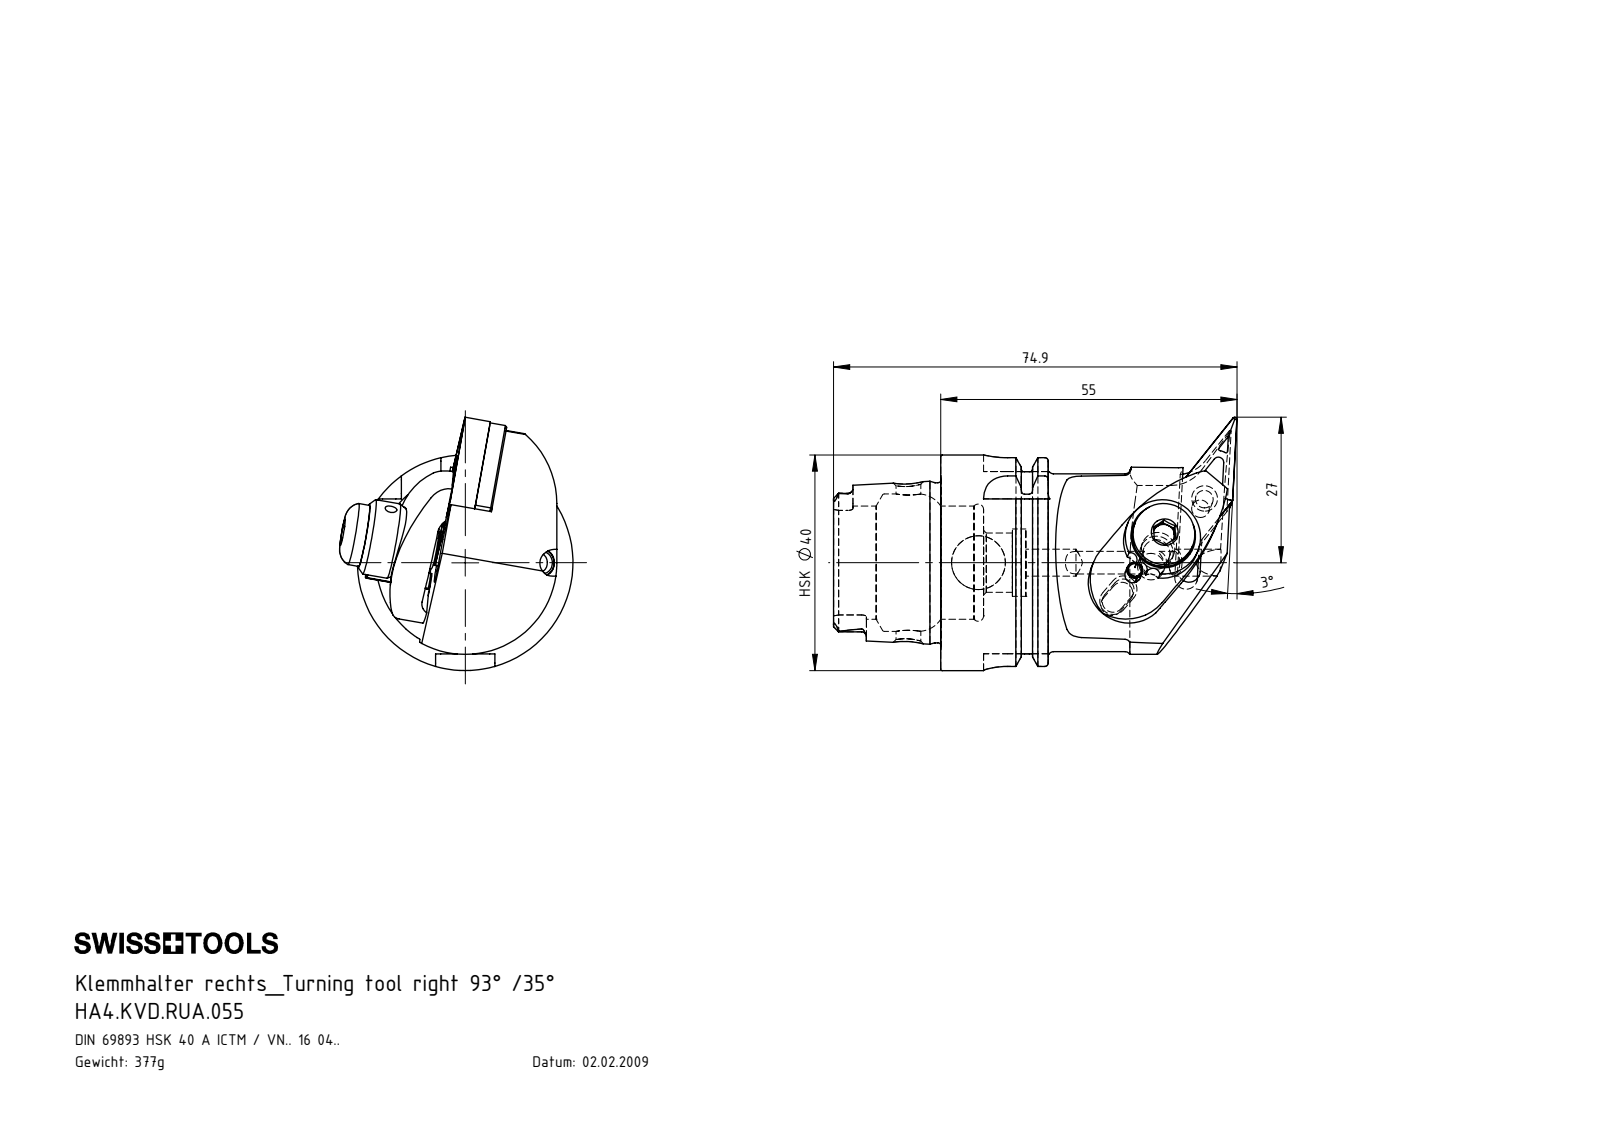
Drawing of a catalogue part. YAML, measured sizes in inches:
part_name: "WCC-ER3.102.024_C; WCC-ER5.102.005_A; VNMG160404; WCC-ER2.001.010_A (+7 more)"
step_written_by: "SolidWorks 2017 (AUTOMOTIVE_DESIGN)"
units: inches
bodies: {solids: 11, faces: 467, planar: 126, cylindrical: 154, other: 187}
overall_size: [2.949, 1.85, 1.706]
volume: 2.898
surface_area: 29.38
round_holes:
  - {diameter: 0.079, count: 3}
  - {diameter: 0.197, count: 2}
  - {diameter: 0.276, count: 2}
  - {diameter: 0.094, count: 1}
  - {diameter: 0.118, count: 1}
  - {diameter: 0.13, count: 1}
  - {diameter: 0.15, count: 1}
  - {diameter: 0.157, count: 1}
  - {diameter: 0.165, count: 1}
  - {diameter: 0.181, count: 1}
  - {diameter: 0.195, count: 1}
  - {diameter: 0.244, count: 1}
round_bosses_or_shafts:
  - {diameter: 0.197, count: 2}
  - {diameter: 0.118, count: 2}
  - {diameter: 1.575, count: 1}
  - {diameter: 1.368, count: 1}
  - {diameter: 1.299, count: 1}
  - {diameter: 1.17, count: 1}
  - {diameter: 0.551, count: 1}
  - {diameter: 0.453, count: 1}
partial_cylinders:
  - {radius: 0.015, count: 6}
  - {radius: 0.035, count: 6}
  - {radius: 0.016, count: 4}
  - {radius: 0.177, count: 4}
  - {radius: 0.027, count: 3}
  - {radius: 0.027, count: 3}
  - {radius: 0.059, count: 3}
  - {radius: 0.118, count: 3}
face_to_face_distances: [0.356, 0.301, 0.176, 0.313, 0.352, 0.051, 0.785, 0.472, 0.375, 0.126]
hole_center_spacings: [0.316, 0.879, 0.563, 0.323, 0.556, 0.556, 0.563]
